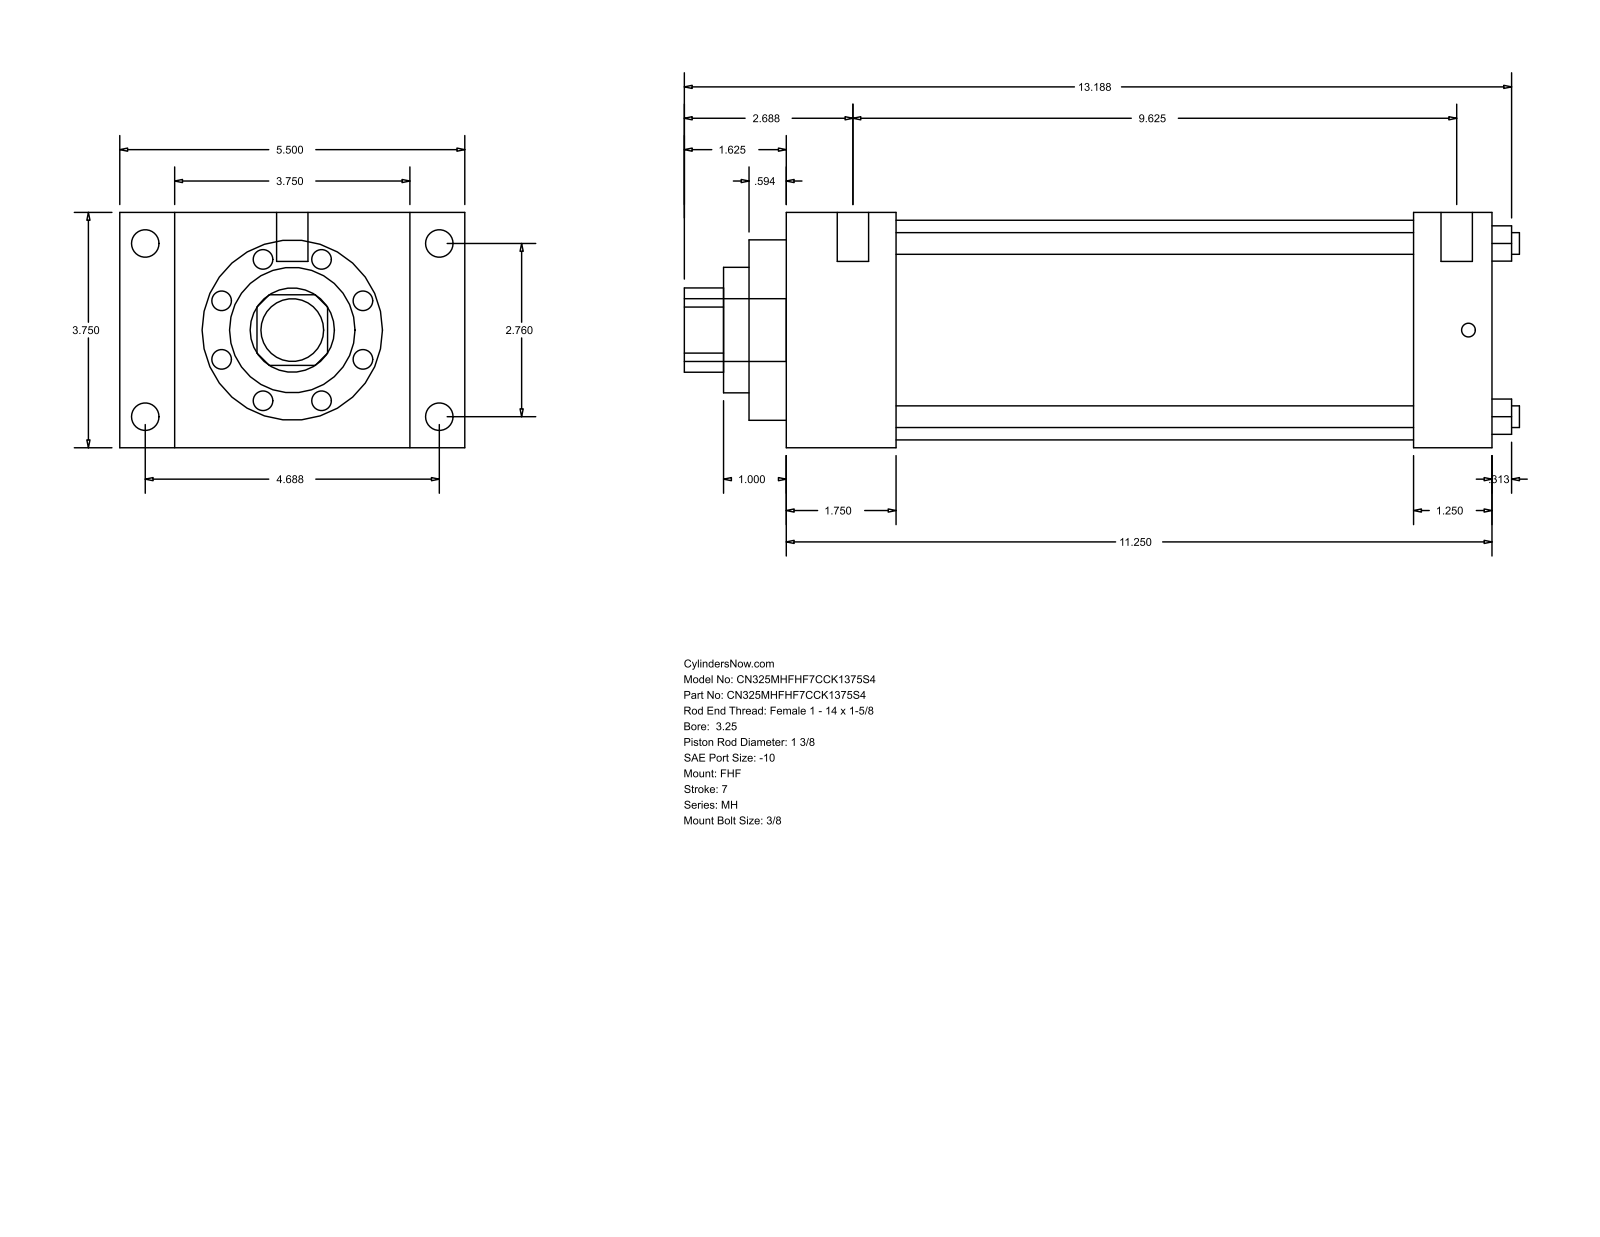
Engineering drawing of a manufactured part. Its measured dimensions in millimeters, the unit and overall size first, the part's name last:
Units: millimetres
Overall size (bounding box): 338.14 × 139.7 × 95.25
Round holes (diameter × count): ⌀8.76 ×4, ⌀34.92 ×1, ⌀50.8 ×1, ⌀73.03 ×1, ⌀88.9 ×1
Round bosses / shafts (diameter × count): ⌀11.13 ×4, ⌀5.56 ×4, ⌀12.7 ×2, ⌀25.4 ×1
Partial cylindrical surfaces — rounded edges, fillets, slot ends (radius × count): R17.06 ×1
Main face-to-face distances: 95.24, 285.75, 44.45, 241.3, 22.23, 117.47, 139.7, 254, 209.55, 31.75
Hole centre spacings: 49.57, 70.1, 99.14
Bodies: 0 solids, 90 faces (61 planar, 29 cylindrical, 0 other)
Part name (STEP PRODUCT): MH_FHF__0325_1.375
STEP written by: GSSL Pune (CONFIG_CONTROL_DESIGN)
